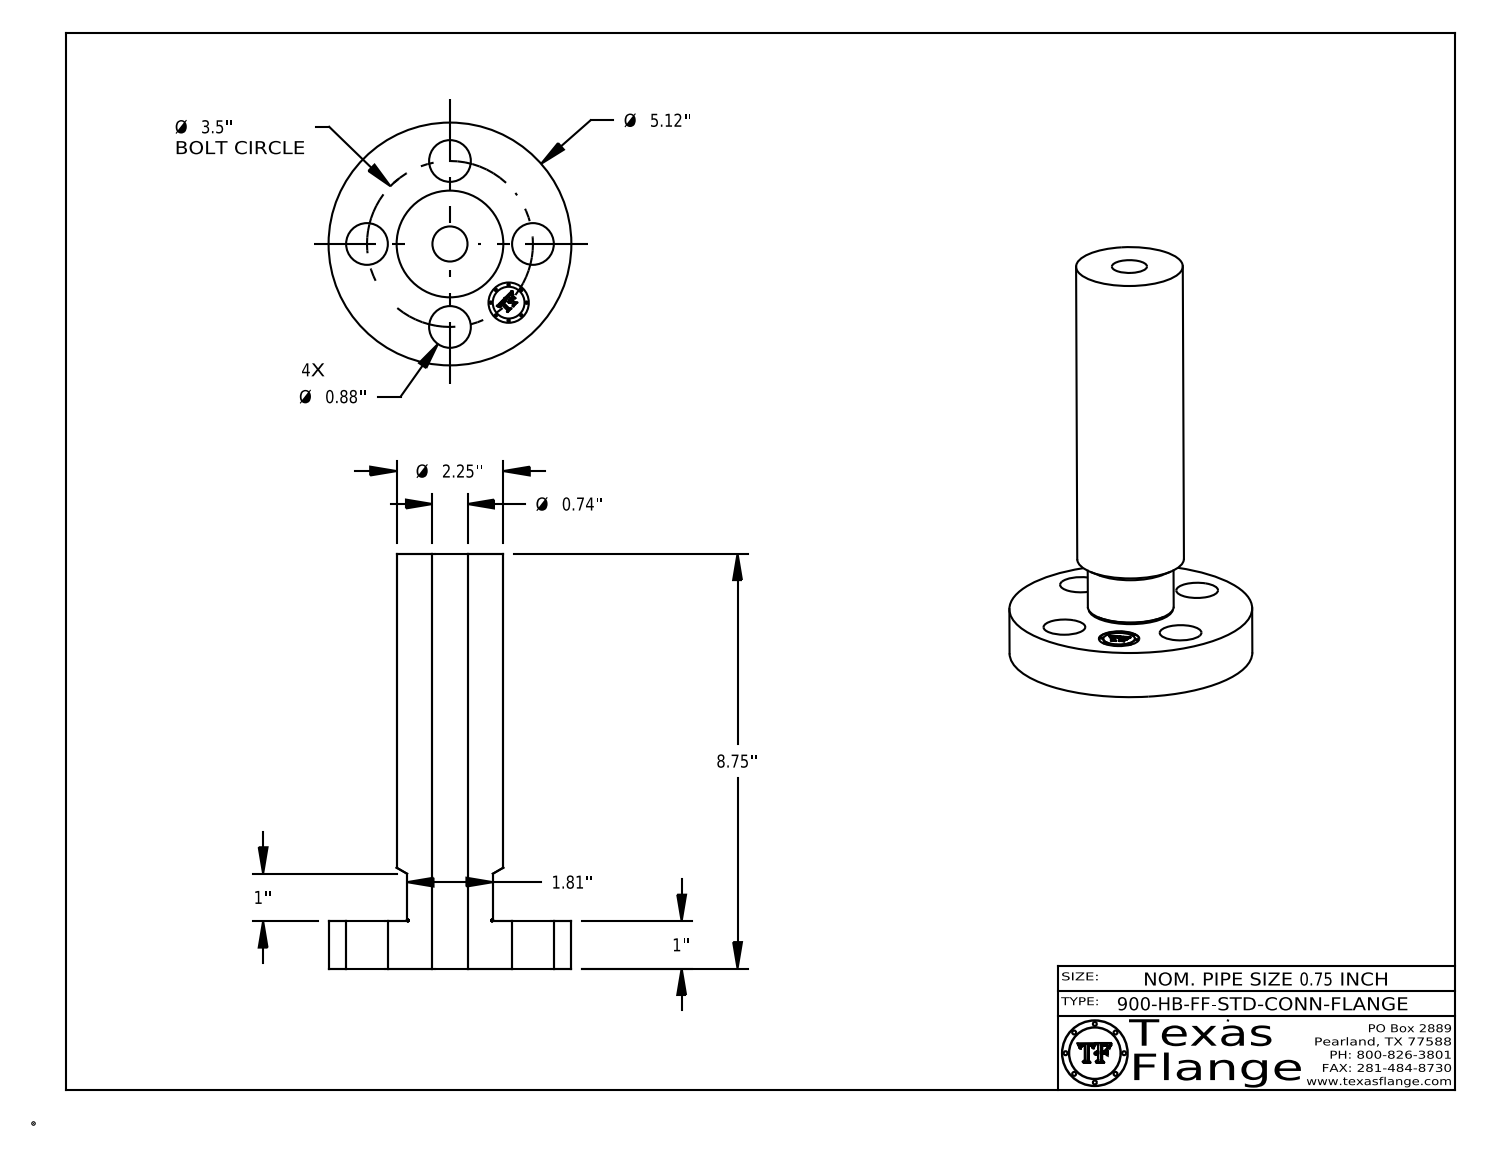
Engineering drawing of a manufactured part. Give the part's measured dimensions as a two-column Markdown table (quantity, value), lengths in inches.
| quantity | value |
| --- | --- |
| part name | 0.75-900-HB-FF-STD-CONN-FLANGE |
| STEP written by | CATIA V5 STEP AP214 (AUTOMOTIVE_DESIGN) |
| units | inches |
| bodies | 1 solid, 410 faces (368 planar, 36 cylindrical, 6 other) |
| overall size | 8.75 × 5.12 × 5.12 |
| volume | 43.71 in³ |
| surface area | 138.7 in² |
| round holes (diameter × count) | 0.88 × 4, 0.74 × 1, 0.85 × 1 |
| round bosses / shafts (diameter × count) | 0.051 × 8, 5.12 × 1, 2.25 × 1, 1.81 × 1, 0.67 × 1 |
| main face-to-face distances | 1, 8.75, 7.75, 0.995, 7.755, 0.016, 0.254, 0.249, 0.046, 0.165 |
| hole center spacings | 1.75, 2.475, 1.339, 3.233, 3.5 |
